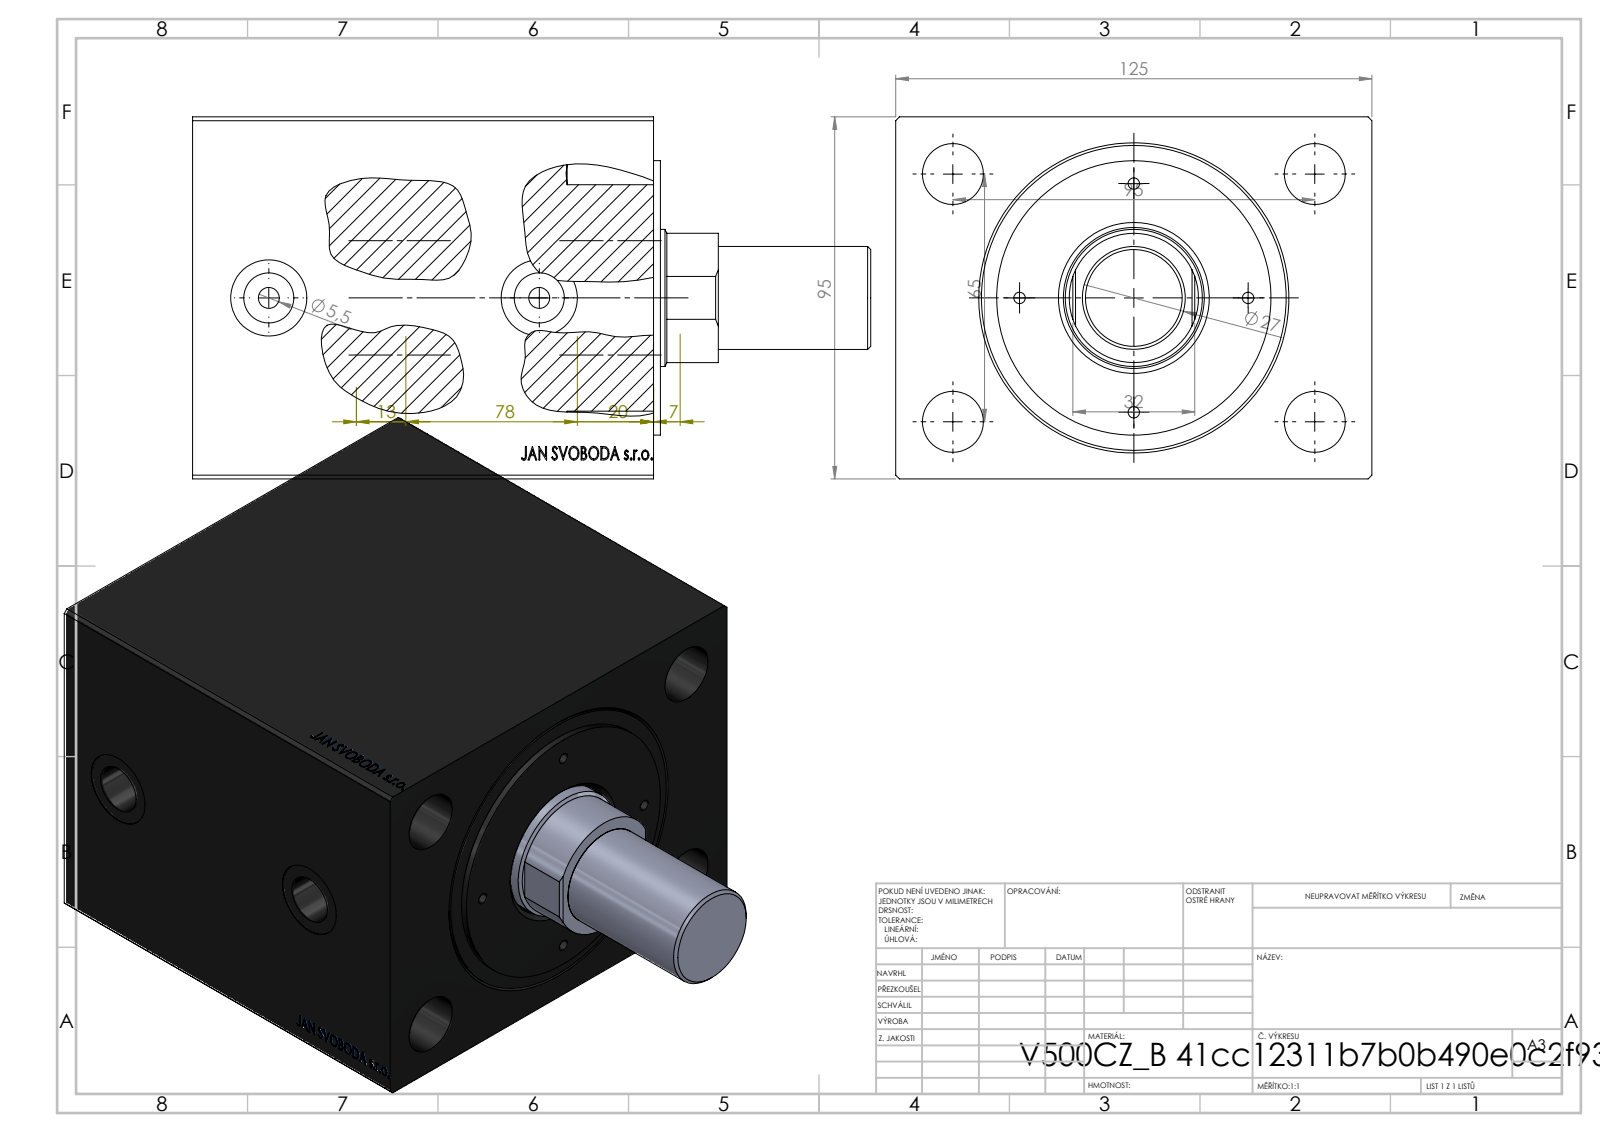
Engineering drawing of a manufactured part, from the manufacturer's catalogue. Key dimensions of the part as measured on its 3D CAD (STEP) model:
Part name (STEP PRODUCT): V500CZ_SMALL_MALE_METRIC; V500CZ; V500CZ_vnitrni_cast_vysunovaci
STEP written by: SolidWorks 2019 (CONFIG_CONTROL_DESIGN)
Units: millimetres
Bodies: 4 solids, 876 faces (403 planar, 61 cylindrical, 412 other)
Overall size (bounding box): 178 × 125 × 95
Volume: 1 362 000 mm³ · Surface area: 136 961 mm²
Round holes (diameter × count): ⌀3 ×4, ⌀16 ×4, ⌀5.5 ×2, ⌀13.16 ×2, ⌀20 ×2, ⌀27 ×1, ⌀36 ×1, ⌀37 ×1, ⌀63 ×1, ⌀80 ×1
Round bosses / shafts (diameter × count): ⌀72 ×1
Partial cylindrical surfaces — rounded edges, fillets, slot ends (radius × count): R16.96 ×1
Main face-to-face distances: 95, 125, 121, 65, 56, 10, 55, 111, 1.8, 11.8
Hole centre spacings: 30, 36.91, 42.43, 47.57, 57.55, 78.5, 84.04, 60
